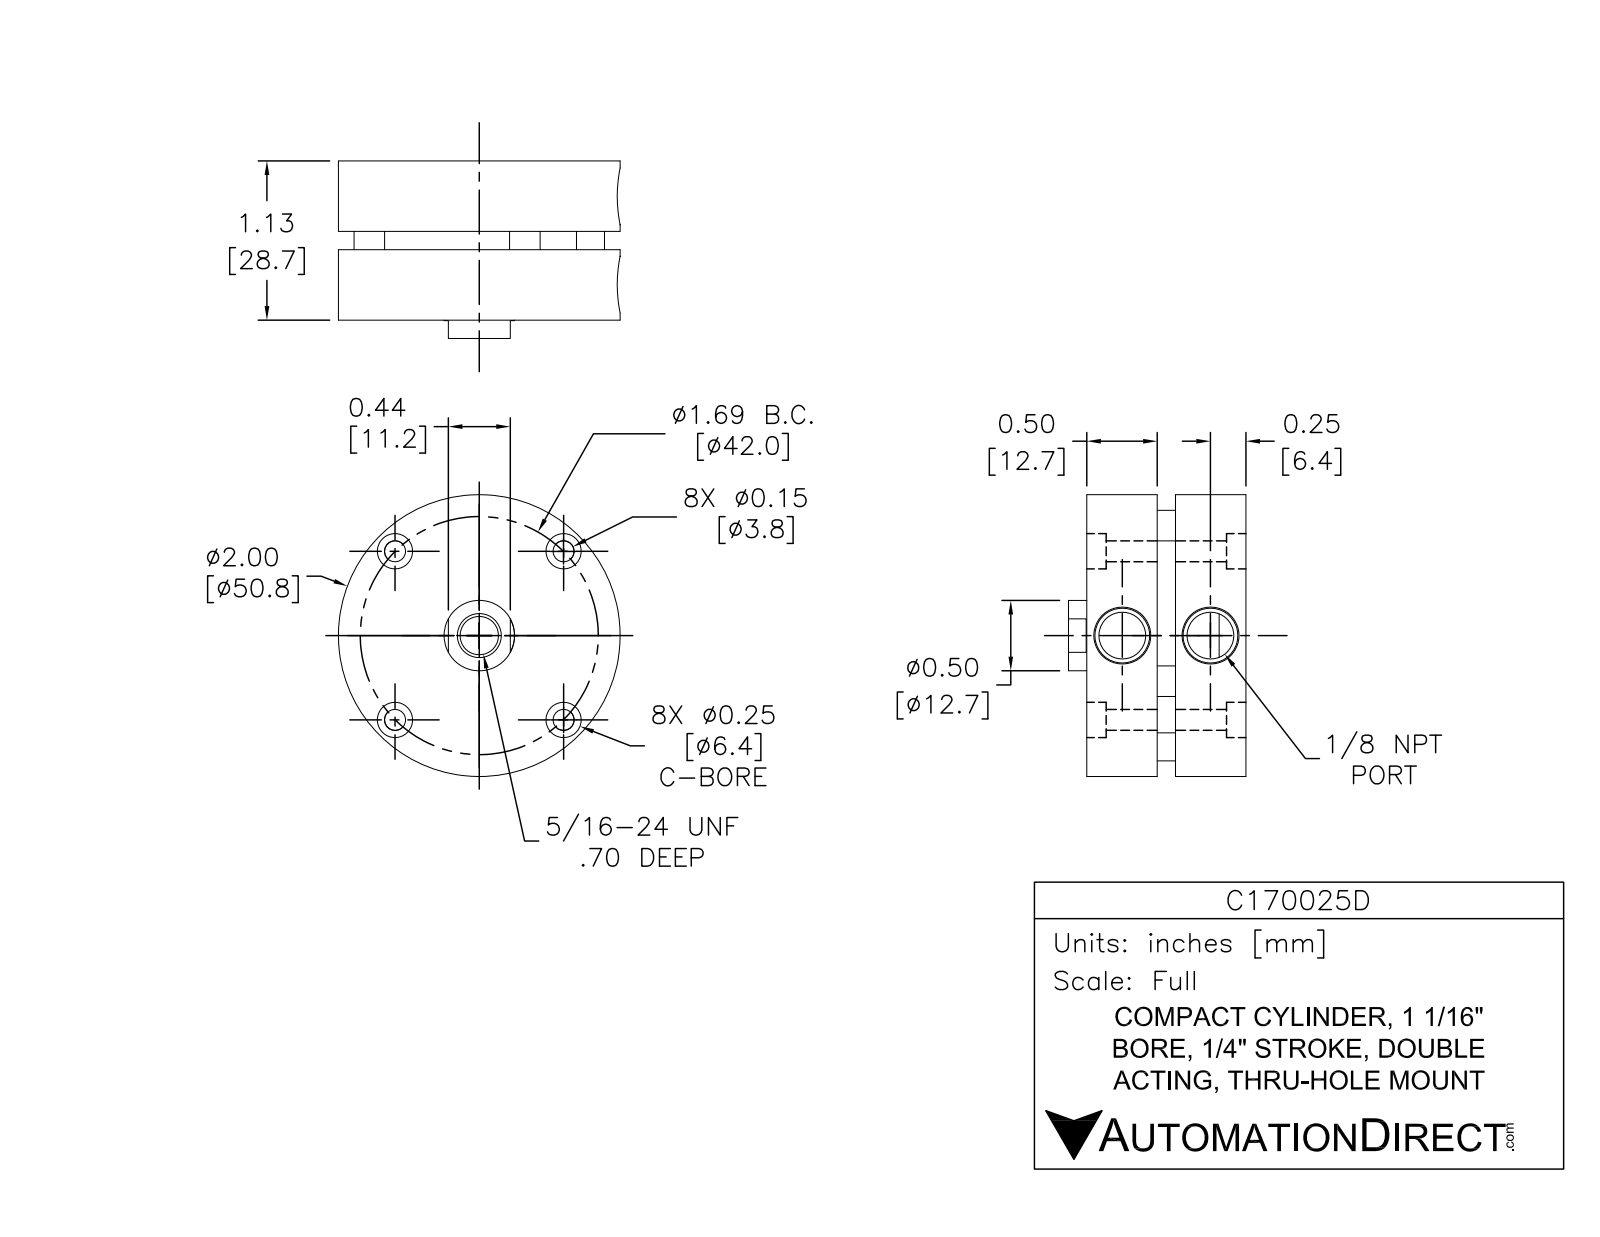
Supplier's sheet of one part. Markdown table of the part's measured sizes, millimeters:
| quantity | value |
| --- | --- |
| part name | C170025D-FO1_BM_r; C170025D-rod_part; C170025D-FO1_BM_rod; C170025D-FO1_BM_heads (2) (+3 more) |
| STEP written by | SolidWorks 2014 (AUTOMOTIVE_DESIGN) |
| units | millimeters |
| bodies | 9 solids, 165 faces (49 planar, 98 cylindrical, 18 other) |
| overall size | 50.8 × 50.8 × 32 |
| volume | 47 850 mm³ |
| surface area | 22 680 mm² |
| round holes (diameter × count) | 3.5 × 4, 4 × 4, 6.4 × 4, 3.2 × 2, 6.8 × 1, 12.7 × 1, 12.8 × 1, 27 × 1, 28.5 × 1 |
| round bosses / shafts (diameter × count) | 6.9 × 4, 50.8 × 1 |
| main face-to-face distances | 16, 12.7, 7.2, 21.5, 5.5, 8.8, 28.7, 3.3, 14.4, 15.2 |
| hole center spacings | 8.4, 21.5, 21.5, 23.9, 30.4, 30.4, 35.7, 42.1 |
